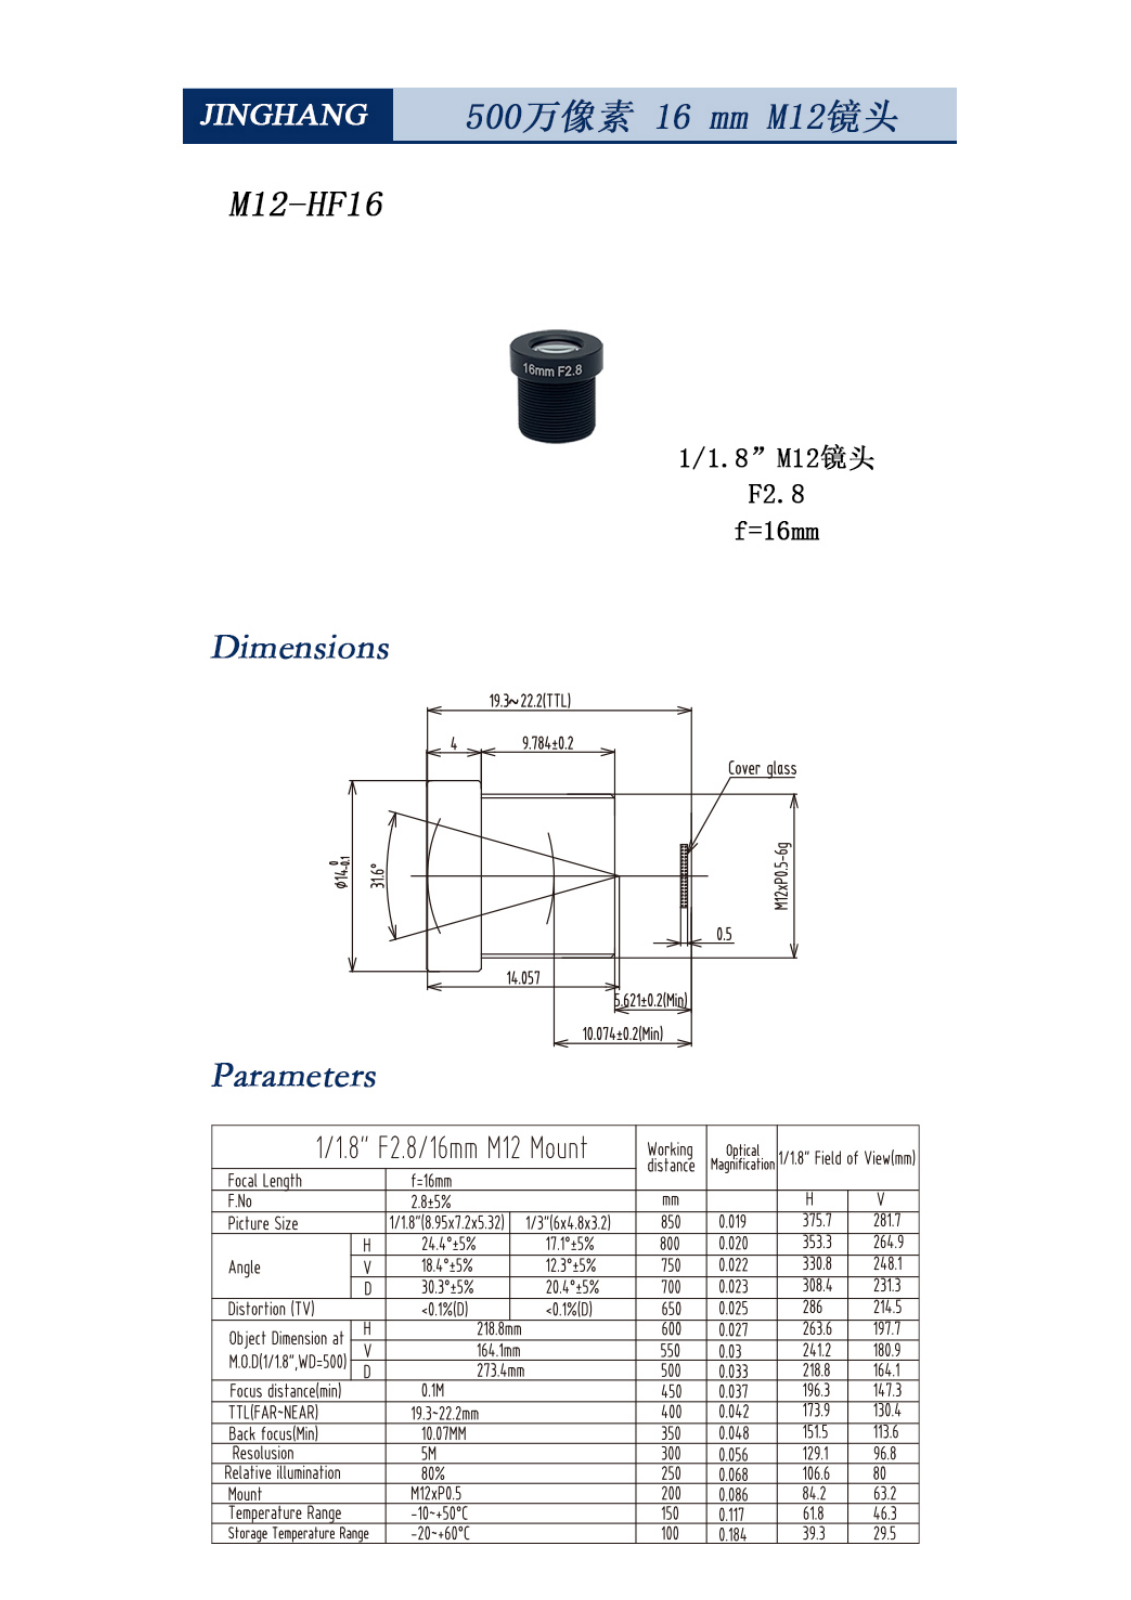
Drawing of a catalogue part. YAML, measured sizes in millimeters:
part_name: "FS1605B"
step_written_by: "PRO/ENGINEER BY PARAMETRIC TECHNOLOGY CORPORATION, 2010370 (CONFIG_CONTROL_DESIGN)"
units: millimeters
bodies: {solids: 2, faces: 91, planar: 8, cylindrical: 48, other: 35}
overall_size: [19.41, 14, 14]
volume: 1552
surface_area: 1247
round_holes:
  - {diameter: 7.6, count: 1}
  - {diameter: 8.8, count: 1}
  - {diameter: 9.86, count: 1}
round_bosses_or_shafts:
  - {diameter: 14, count: 1}
  - {diameter: 12, count: 1}
  - {diameter: 9.22, count: 1}
face_to_face_distances: [19.41, 19.4, 6.89, 6.88, 12.52, 15.41, 15.4, 8.52, 4, 5.63]
